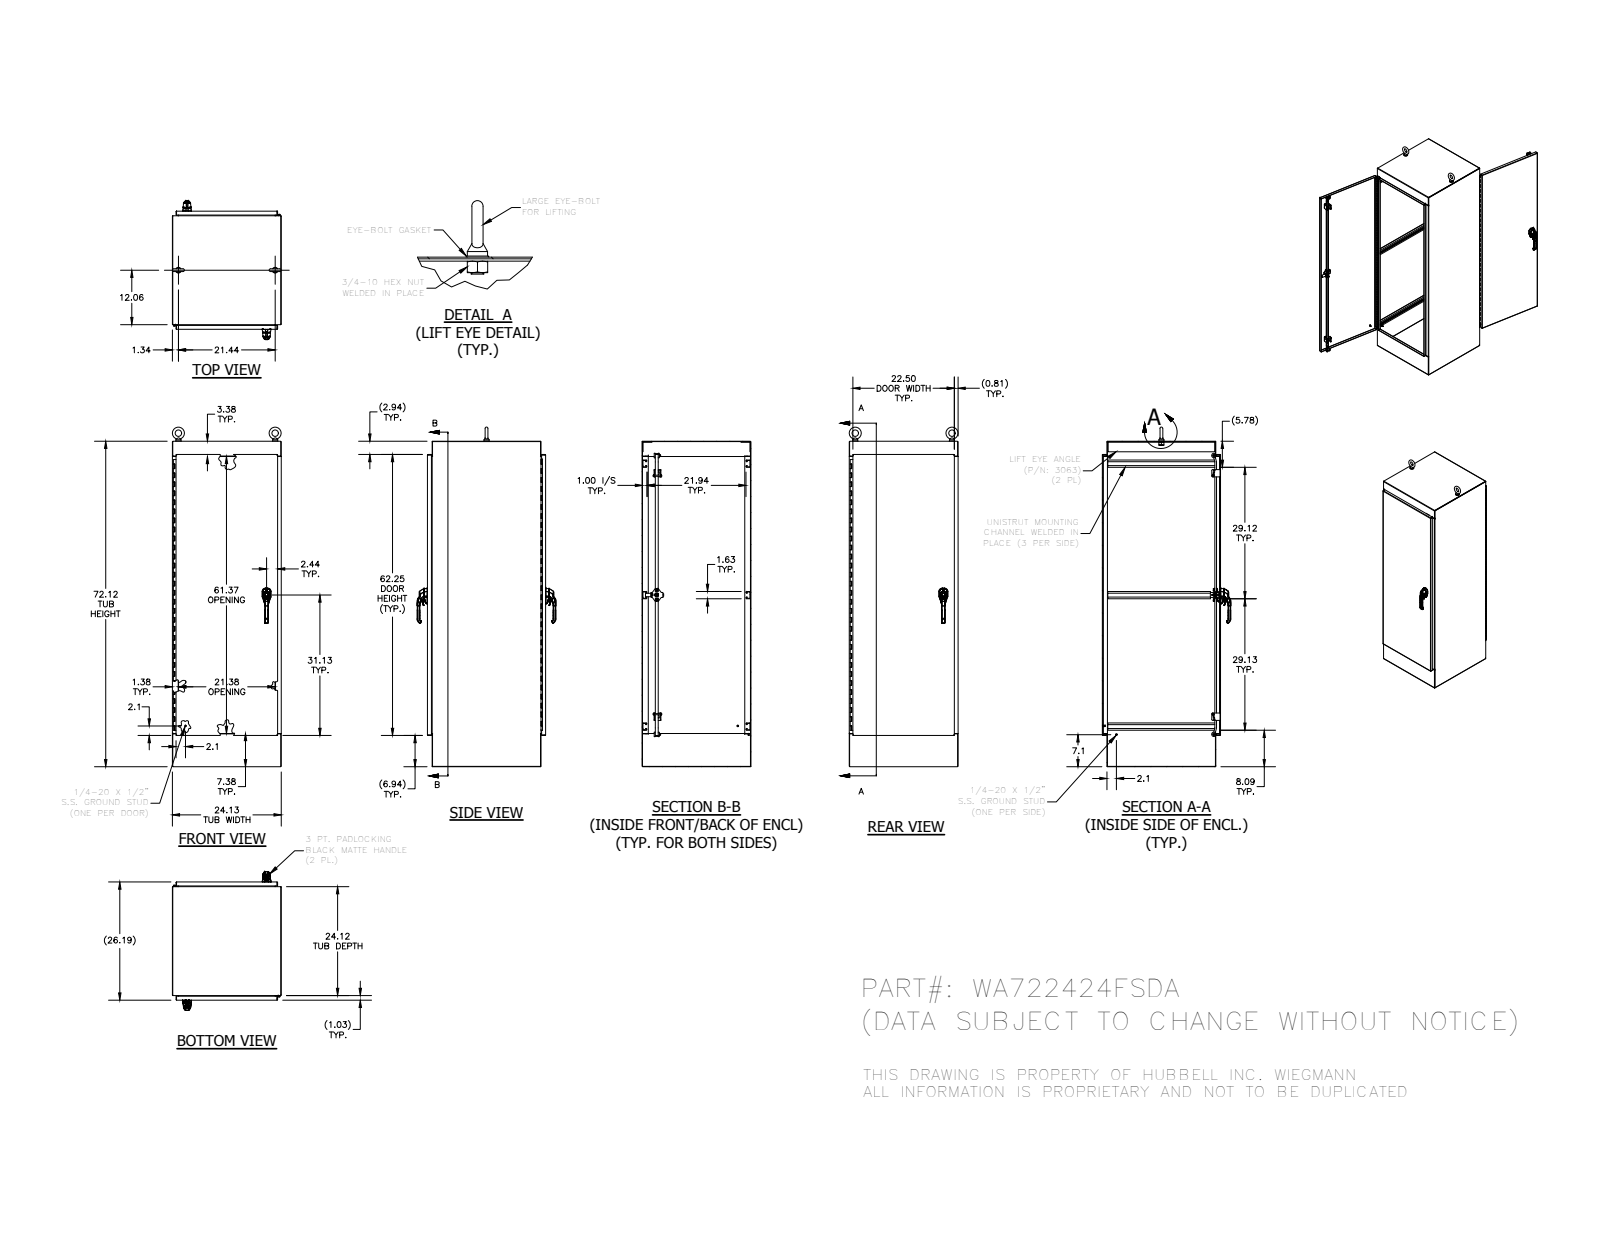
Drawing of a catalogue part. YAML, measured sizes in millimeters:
part_name: "WA7224FSDALRS; WA2424FSDABTM; WA2424FSDATOP; WA7224FSDADR (+8 more)"
step_written_by: "Autodesk Inventor 2014 (AUTOMOTIVE_DESIGN)"
units: millimeters
bodies: {solids: 84, faces: 5638, planar: 2368, cylindrical: 2004, other: 1266}
overall_size: [1911.29, 780.41, 612.77]
volume: 15520000
surface_area: 13290000
round_holes:
  - {diameter: 7.02, count: 16}
  - {diameter: 5.08, count: 8}
  - {diameter: 5.4, count: 6}
  - {diameter: 6, count: 6}
  - {diameter: 7.11, count: 6}
  - {diameter: 6.13, count: 4}
  - {diameter: 6.35, count: 4}
  - {diameter: 6.41, count: 4}
  - {diameter: 10.16, count: 4}
  - {diameter: 10.33, count: 4}
  - {diameter: 10.5, count: 4}
  - {diameter: 11.43, count: 4}
round_bosses_or_shafts:
  - {diameter: 6.35, count: 6}
  - {diameter: 25.4, count: 4}
  - {diameter: 14.29, count: 4}
  - {diameter: 13.37, count: 4}
  - {diameter: 12.7, count: 4}
  - {diameter: 9.52, count: 4}
  - {diameter: 8.56, count: 4}
  - {diameter: 7.94, count: 4}
partial_cylinders:
  - {radius: 0.5, count: 332}
  - {radius: 0.3, count: 169}
  - {radius: 0.47, count: 38}
  - {radius: 0.25, count: 32}
  - {radius: 2, count: 30}
  - {radius: 1.27, count: 28}
  - {radius: 0.79, count: 26}
  - {radius: 3, count: 24}
face_to_face_distances: [2.38, 610.4, 662.79, 608.02, 612.78, 660.41, 665.17, 1829.59, 26.3, 26.09]
hole_center_spacings: [447.64, 9.66, 9.7, 9.71, 12.5, 19.36, 19.4, 22.5]
